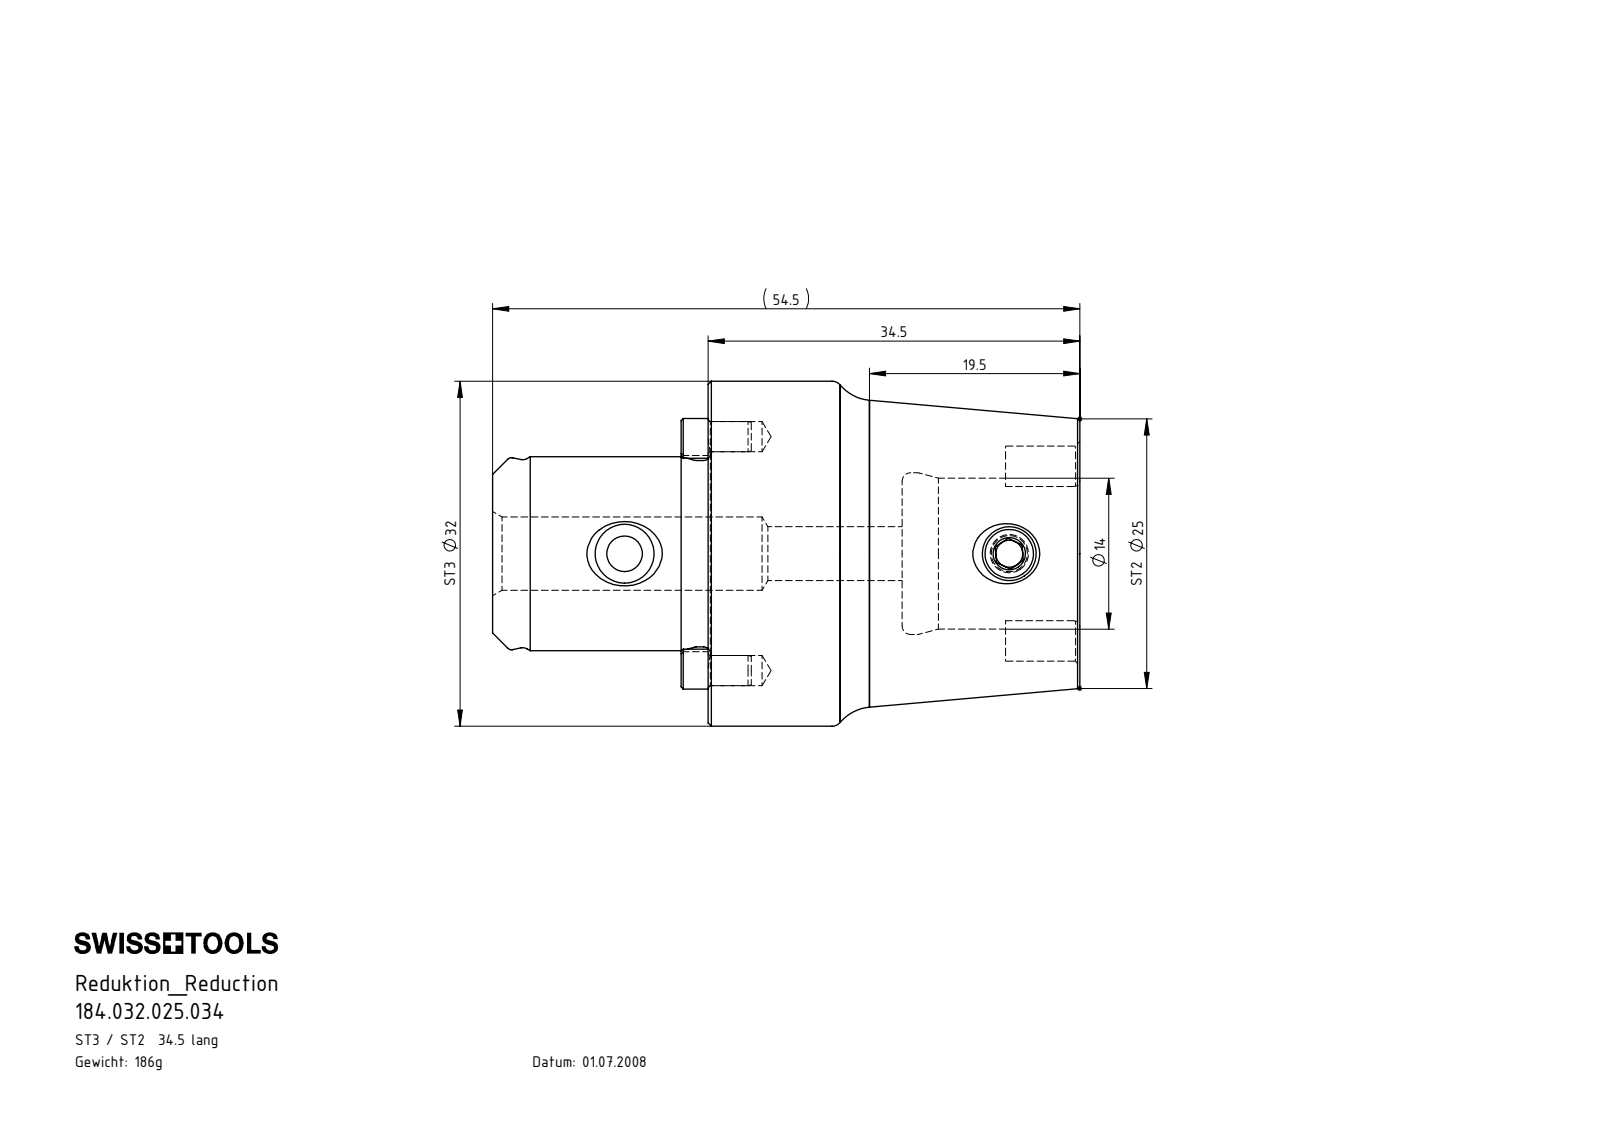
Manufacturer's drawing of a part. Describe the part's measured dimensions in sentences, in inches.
The part is named "ST3-ST2.K01.034; ST3-ER2.001.007_A; ST2-ER1.001.006_A; ST3-ST2.K01.034_A". Its 3-D file was written by "SolidWorks 2015 (CONFIG_CONTROL_DESIGN)". It is 4 solids with 160 faces: 26 planar, 45 cylindrical and 89 other. Overall it measures 2.146 by 1.26 by 1.26 inches. Its volume is 1.444 cubic inches and its surface area 11.68 square inches. Round holes: 2 of diameter 0.11, 1 of diameter 0.13, 1 of diameter 0.177, 1 of diameter 0.197, 1 of diameter 0.268, 1 of diameter 0.551, 1 of diameter 0.591. Round bosses or shafts: 1 of diameter 1.26, 1 of diameter 0.709, 1 of diameter 0.701, 1 of diameter 0.681, 1 of diameter 0.197. Partial cylindrical surfaces (rounded edges, fillets, slot ends): 4 of radius 0.02, 2 of radius 0.071, 2 of radius 0.107, 2 of radius 0.356. The main face-to-face distances are 1.358, 0.787, 2.146, 1.496, 0.709, 0.65, 0.464, 0.098, 0.689, 0.807. The hole center spacings are 0.427, 0.854, 1.406.
